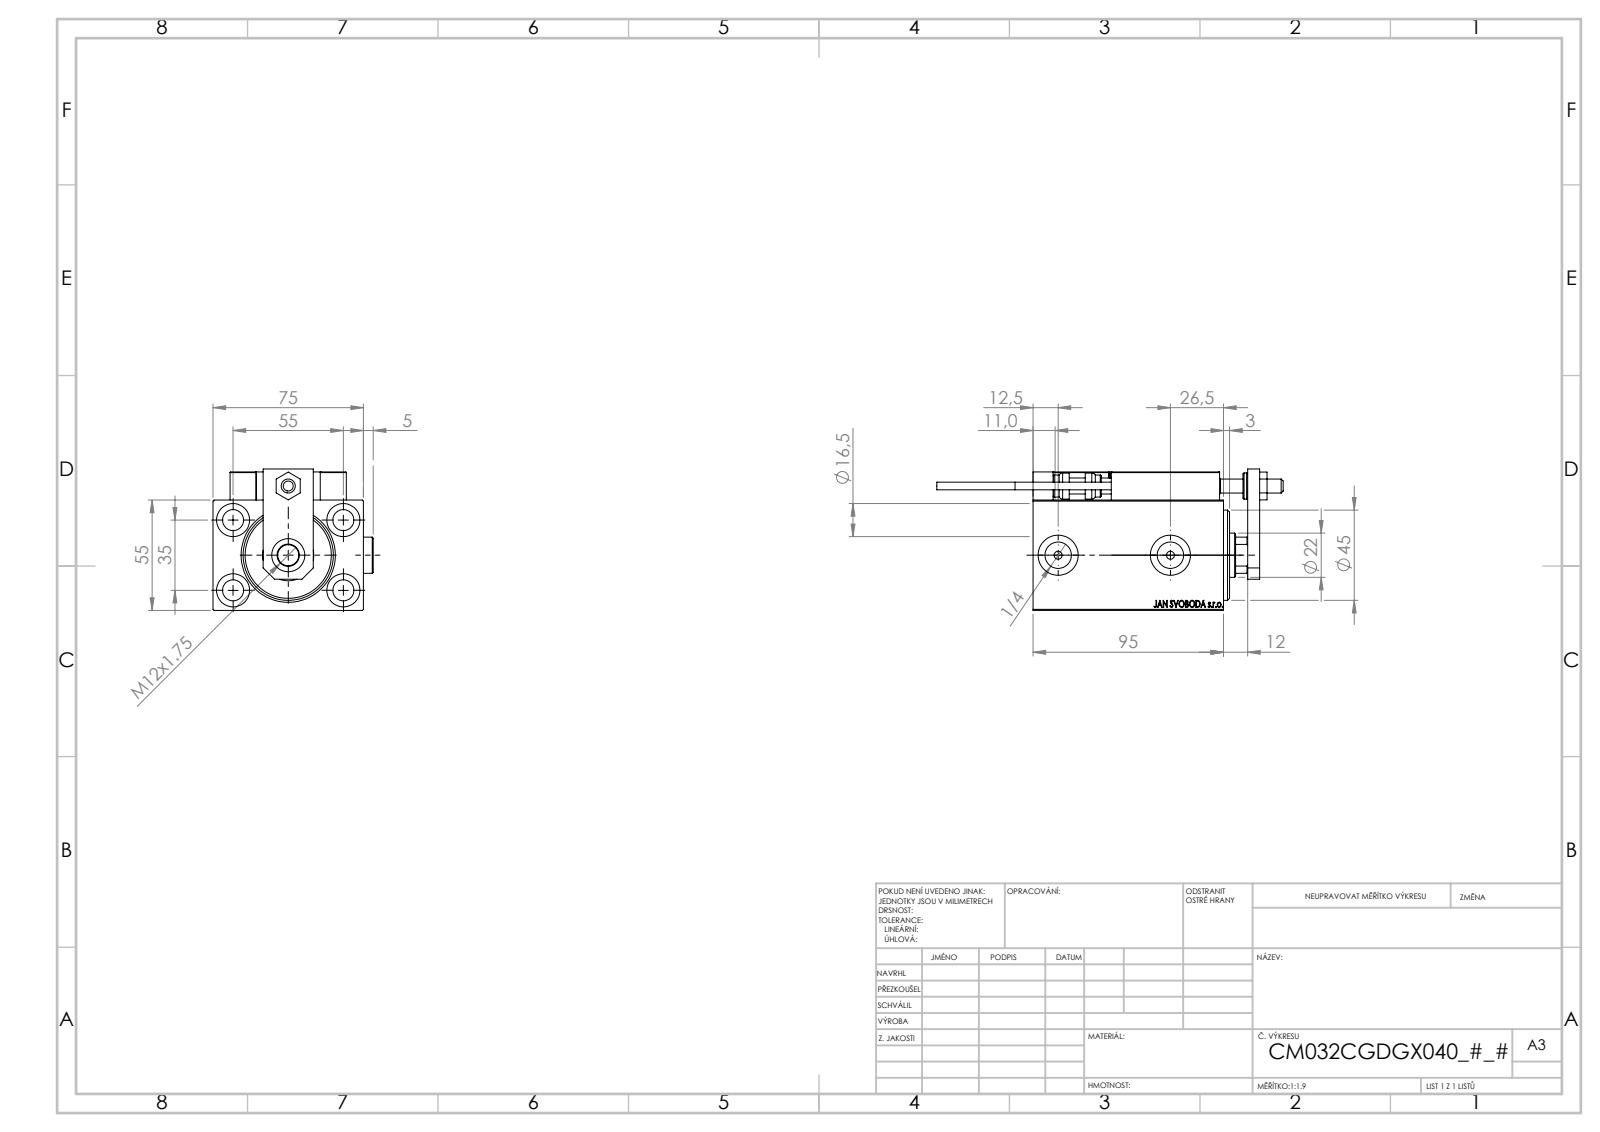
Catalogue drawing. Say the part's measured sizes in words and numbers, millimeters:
The part is named "V450CM_VC_B; ALLEN BOLT D8; MAGNET; SWITCH X (+8 more)". Its 3-D file was written by "SolidWorks 2019 (CONFIG_CONTROL_DESIGN)". It is 25 solids with 1336 faces: 594 planar, 204 cylindrical and 538 other. Overall it measures 172.7 by 79.9 by 70.5 millimeters. Its volume is 379 782 cubic millimeters and its surface area 99 131 square millimeters. Round holes: 6 of diameter 4, 5 of diameter 8, 5 of diameter 10.5, 5 of diameter 16.5, 4 of diameter 3.2, 2 of diameter 5, 2 of diameter 13.16, 2 of diameter 20, 1 of diameter 7, 1 of diameter 22, 1 of diameter 25.5, 1 of diameter 32. Round bosses or shafts: 2 of diameter 18, 2 of diameter 5, 2 of diameter 3.8, 1 of diameter 13, 1 of diameter 11. Partial cylindrical surfaces (rounded edges, fillets, slot ends): 30 of radius 0.3, 2 of radius 3, 1 of radius 10.5. The main face-to-face distances are 55, 75, 14, 10, 12, 5, 69, 7, 15, 25. The hole center spacings are 32.6, 11.37, 20, 29.59, 29.69, 32.33, 35, 36.06.
